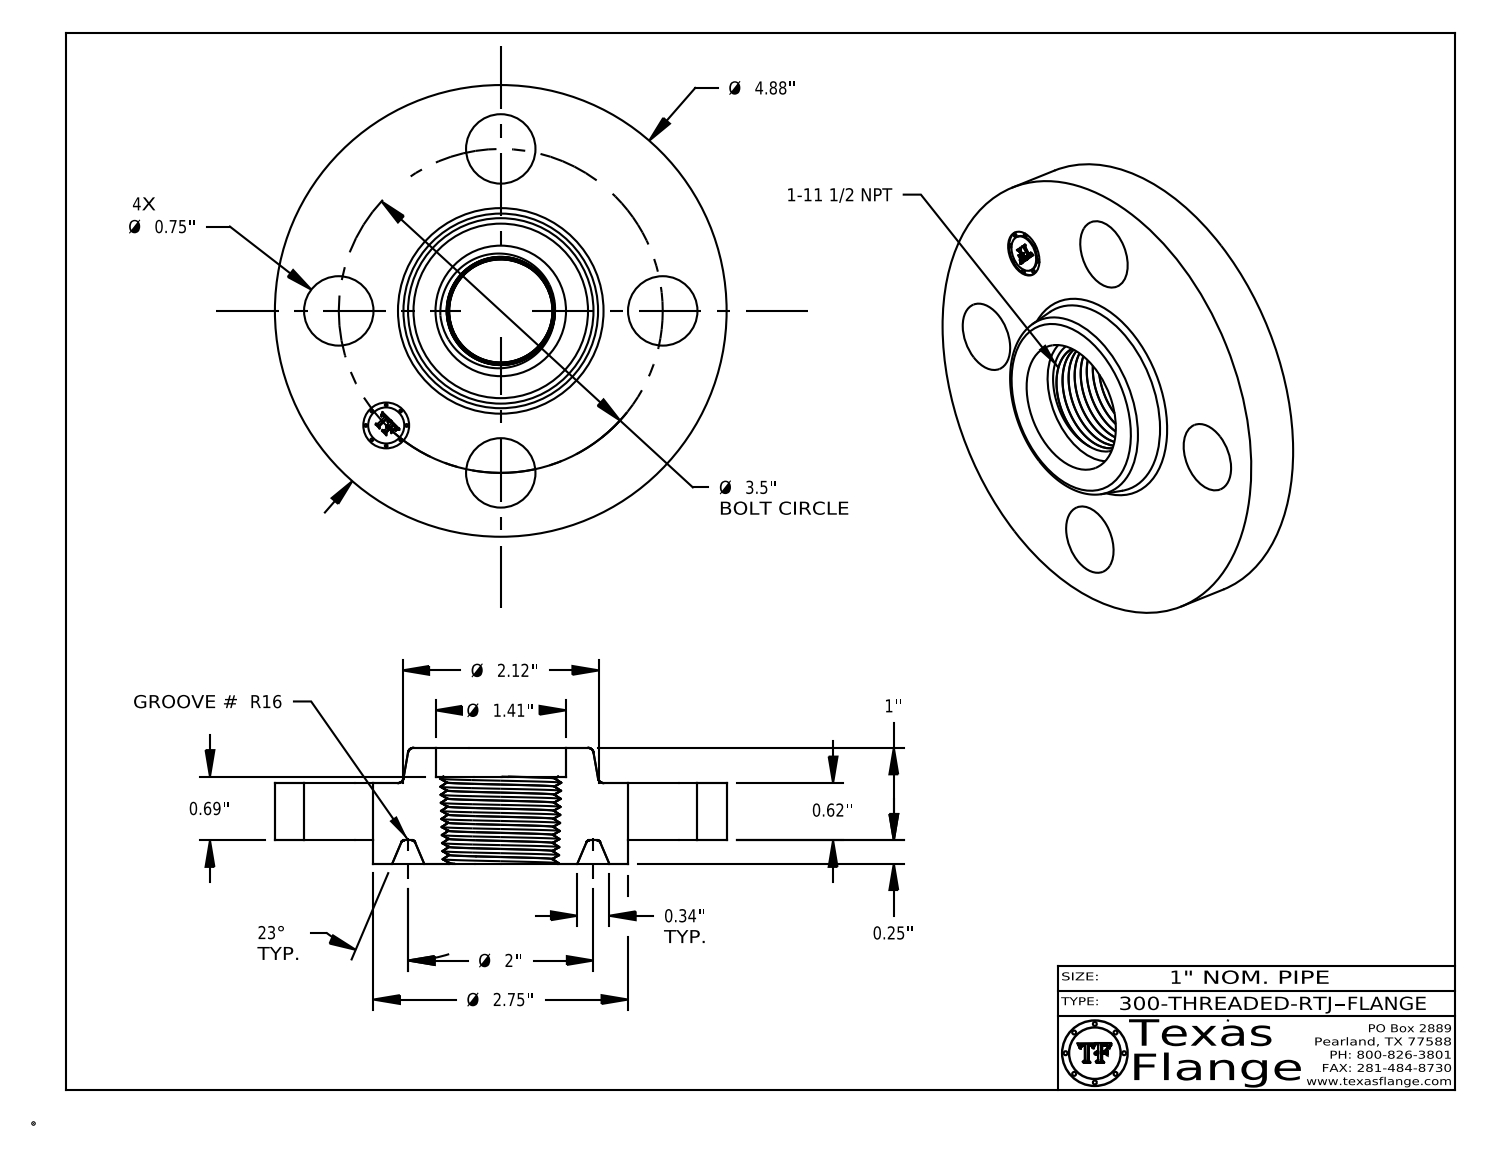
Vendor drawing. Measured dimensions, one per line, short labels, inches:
name: 300-THREADED-RTJ
written by: CATIA V5 STEP AP214 (AUTOMOTIVE_DESIGN)
unit: in
bodies: 1 solid, 533 faces (372 planar, 34 cylindrical, 127 other)
size: 4.88 × 4.88 × 1.25
volume: 11.31 in³; area: 61.09 in²
holes: 4× ⌀0.75, 1× ⌀0.495, 1× ⌀1.41
bosses: 8× ⌀0.03, 1× ⌀4.88, 1× ⌀2.75, 1× ⌀0.39
face distances: 0.62, 0.25, 0.87, 1.25, 1, 0.38, 0.07, 0.94, 0.69, 0.31
hole spacings: 1.75, 2.475, 1.339, 3.233, 3.5
